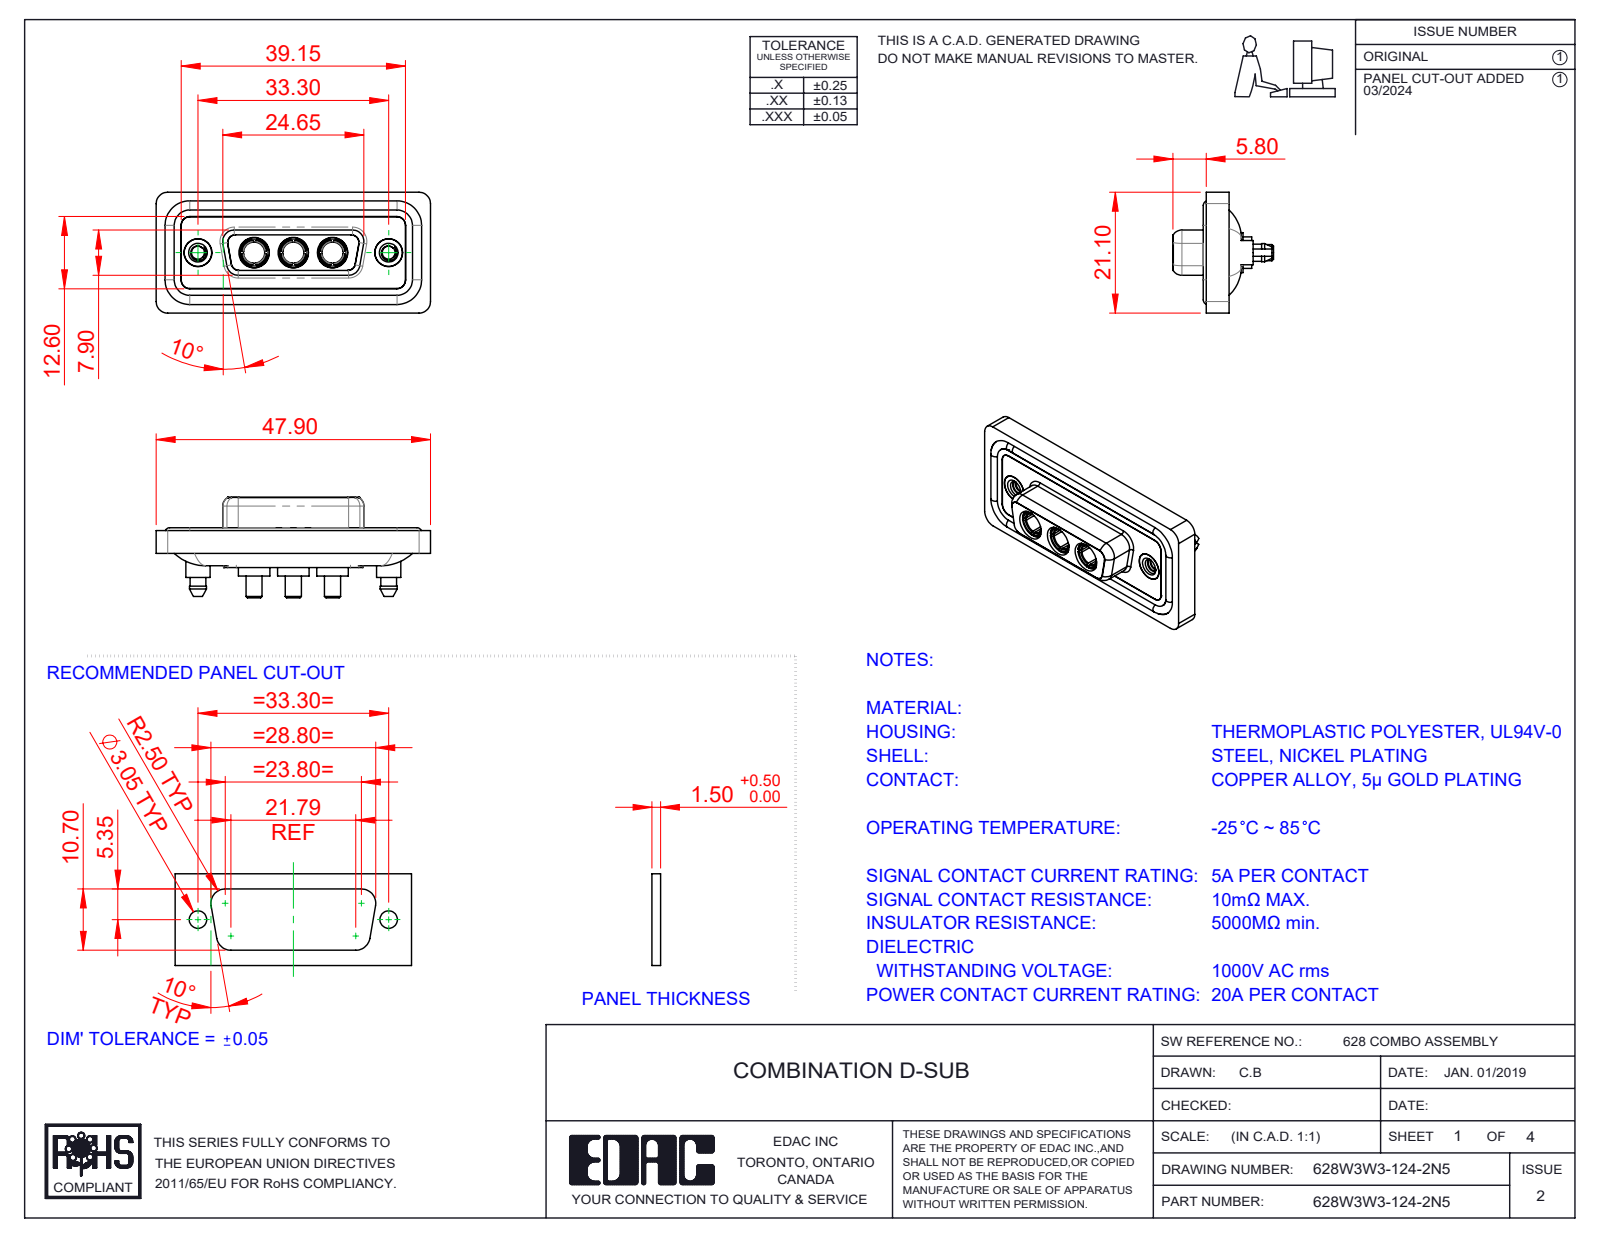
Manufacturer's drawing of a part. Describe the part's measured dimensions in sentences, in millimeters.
The part is named "628Combo Housing_3W3; 628W3W3-124-2N5; 628Combo Shell Front_15 Contacts; 628Combo Shell Rear_15 Contacts (+3 more)". Its 3-D file was written by "SolidWorks 2023 (CONFIG_CONTROL_DESIGN)". It is 13 solids with 658 faces: 208 planar, 289 cylindrical and 161 other. Overall it measures 47.9 by 21.1 by 17.55 millimeters. Its volume is 6 160 cubic millimeters and its surface area 10 072 square millimeters. Round holes: 5 of diameter 4.85, 3 of diameter 3.7, 3 of diameter 5.3, 2 of diameter 2.26, 2 of diameter 4, 2 of diameter 4.05, 2 of diameter 5. Round bosses or shafts: 4 of diameter 1.6, 3 of diameter 5.5, 3 of diameter 5.2, 3 of diameter 4.96, 3 of diameter 4.75, 3 of diameter 3.75, 3 of diameter 2.8, 2 of diameter 5.4. Partial cylindrical surfaces (rounded edges, fillets, slot ends): 24 of radius 1.5, 20 of radius 2, 12 of radius 1.35, 10 of radius 1.6, 4 of radius 0.25, 4 of radius 0.5, 4 of radius 0.6, 4 of radius 0.65. The main face-to-face distances are 0.4, 1.8, 1.6, 0.5, 7.45, 1.1, 2.9, 5.65, 7.05, 6.6. The hole center spacings are 6.85, 9.8, 16.65, 23.5, 13.7, 33.3.
